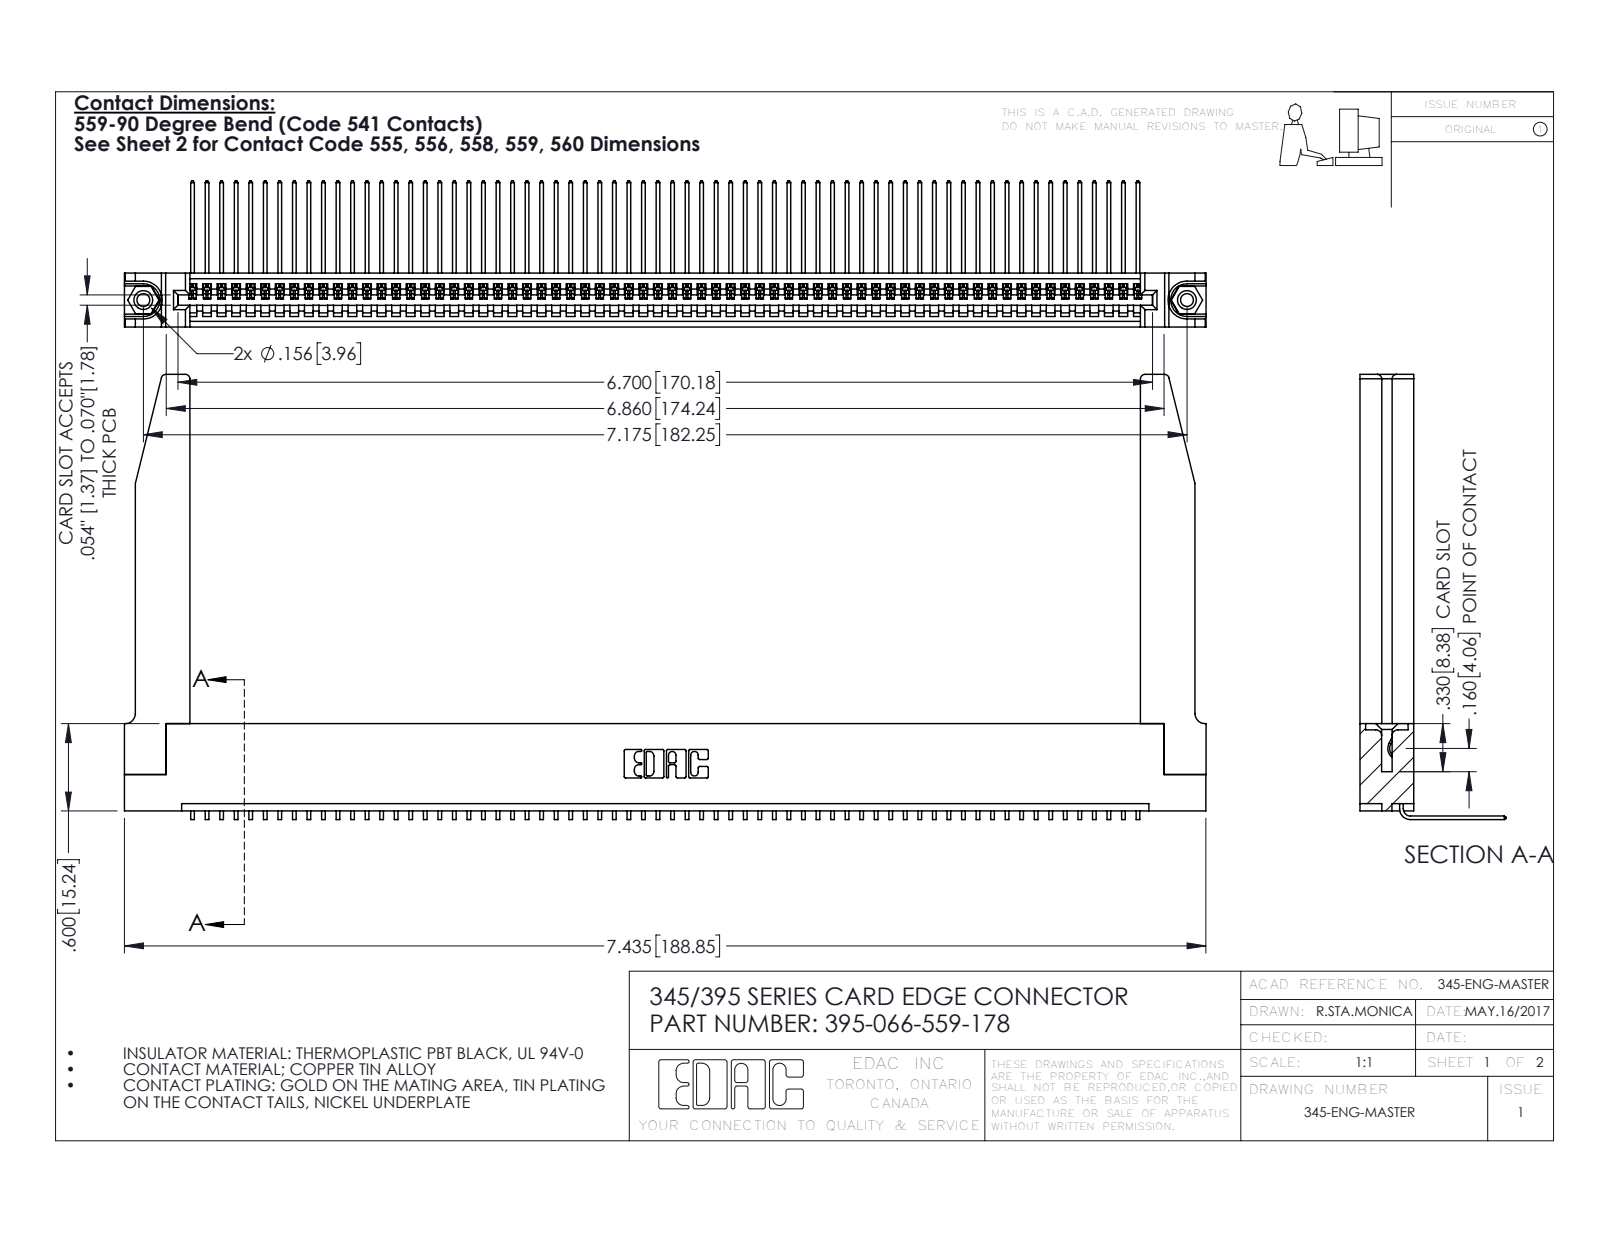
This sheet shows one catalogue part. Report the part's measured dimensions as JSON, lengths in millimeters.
{"part_name": "345-220-078_345-220-078; 345-250-001_345-250-001-102; 345-292-001_558 559 Tail - 1; 345 Part_Flush Mounting Lugs - 0.156 Dia-TH (+1 more)", "step_written_by": "SolidWorks 2016 (CONFIG_CONTROL_DESIGN)", "units": "millimeters", "bodies": {"solids": 71, "faces": 4320, "planar": 2994, "cylindrical": 1274, "other": 52}, "overall_size": [188.9, 77.7, 25.5], "volume_mm3": 26120, "surface_area_mm2": 32860, "round_holes": [[2.3, 2], [3.2, 2], [4, 2], [1.6, 1]], "round_bosses_or_shafts": [[3.9, 2]], "partial_cylinders_radius": [[0.2, 132], [0.3, 22], [0.8, 8], [0.2, 6], [0.8, 6], [0.7, 3], [0.8, 2], [1, 2]], "face_to_face_distances": [9.4, 1.8, 7.6, 5.1, 2.5, 6.9, 0.6, 5.7, 3.8, 3.8], "hole_center_spacings": [6.9, 176.3, 182.2]}
